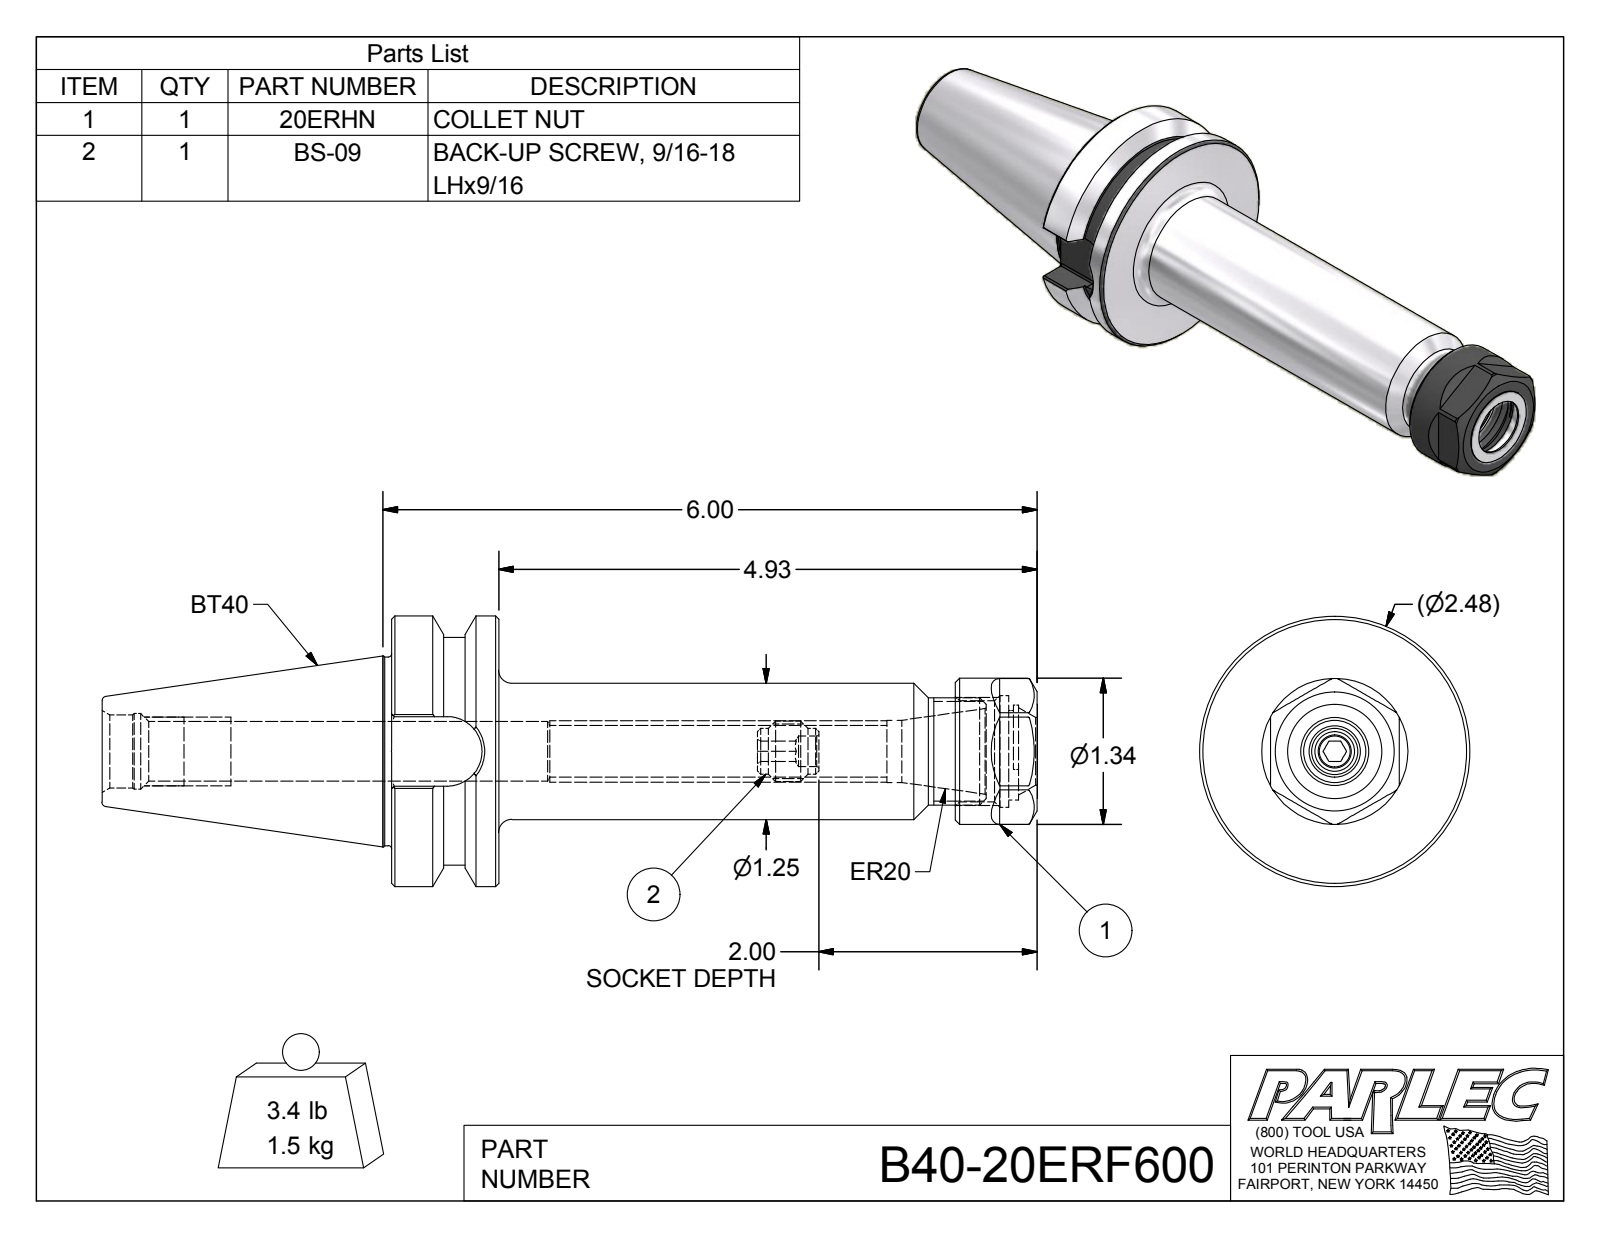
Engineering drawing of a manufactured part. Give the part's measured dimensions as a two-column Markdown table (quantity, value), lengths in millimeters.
| quantity | value |
| --- | --- |
| part name | B40-20ER6-1; 20ERHN; BS-09; B40-20ERF600 |
| STEP written by | Autodesk Inventor 2016 (AUTOMOTIVE_DESIGN) |
| units | millimeters |
| bodies | 3 solids, 130 faces (55 planar, 34 cylindrical, 41 other) |
| overall size | 217.81 × 62.99 × 62.99 |
| volume | 198 534 mm³ |
| surface area | 43 125 mm² |
| round holes (diameter × count) | 7.14 × 1, 11.99 × 1, 13.84 × 1, 14.48 × 1, 15.49 × 1, 17.01 × 1, 17.62 × 1, 23.5 × 1, 26 × 1 |
| round bosses / shafts (diameter × count) | 62.99 × 1, 53.01 × 1, 43.94 × 1, 34 × 1, 31.75 × 1, 25 × 1, 14.1 × 1, 10.72 × 1 |
| partial cylindrical surfaces (radius × count) | 0.51 × 8, 8.09 × 1, 9.47 × 1, 10.55 × 1, 10.75 × 1 |
| main face-to-face distances | 24.99, 150.42, 125.43, 30, 131.35, 106.36, 19.07, 45.22, 7.61, 37.61 |
